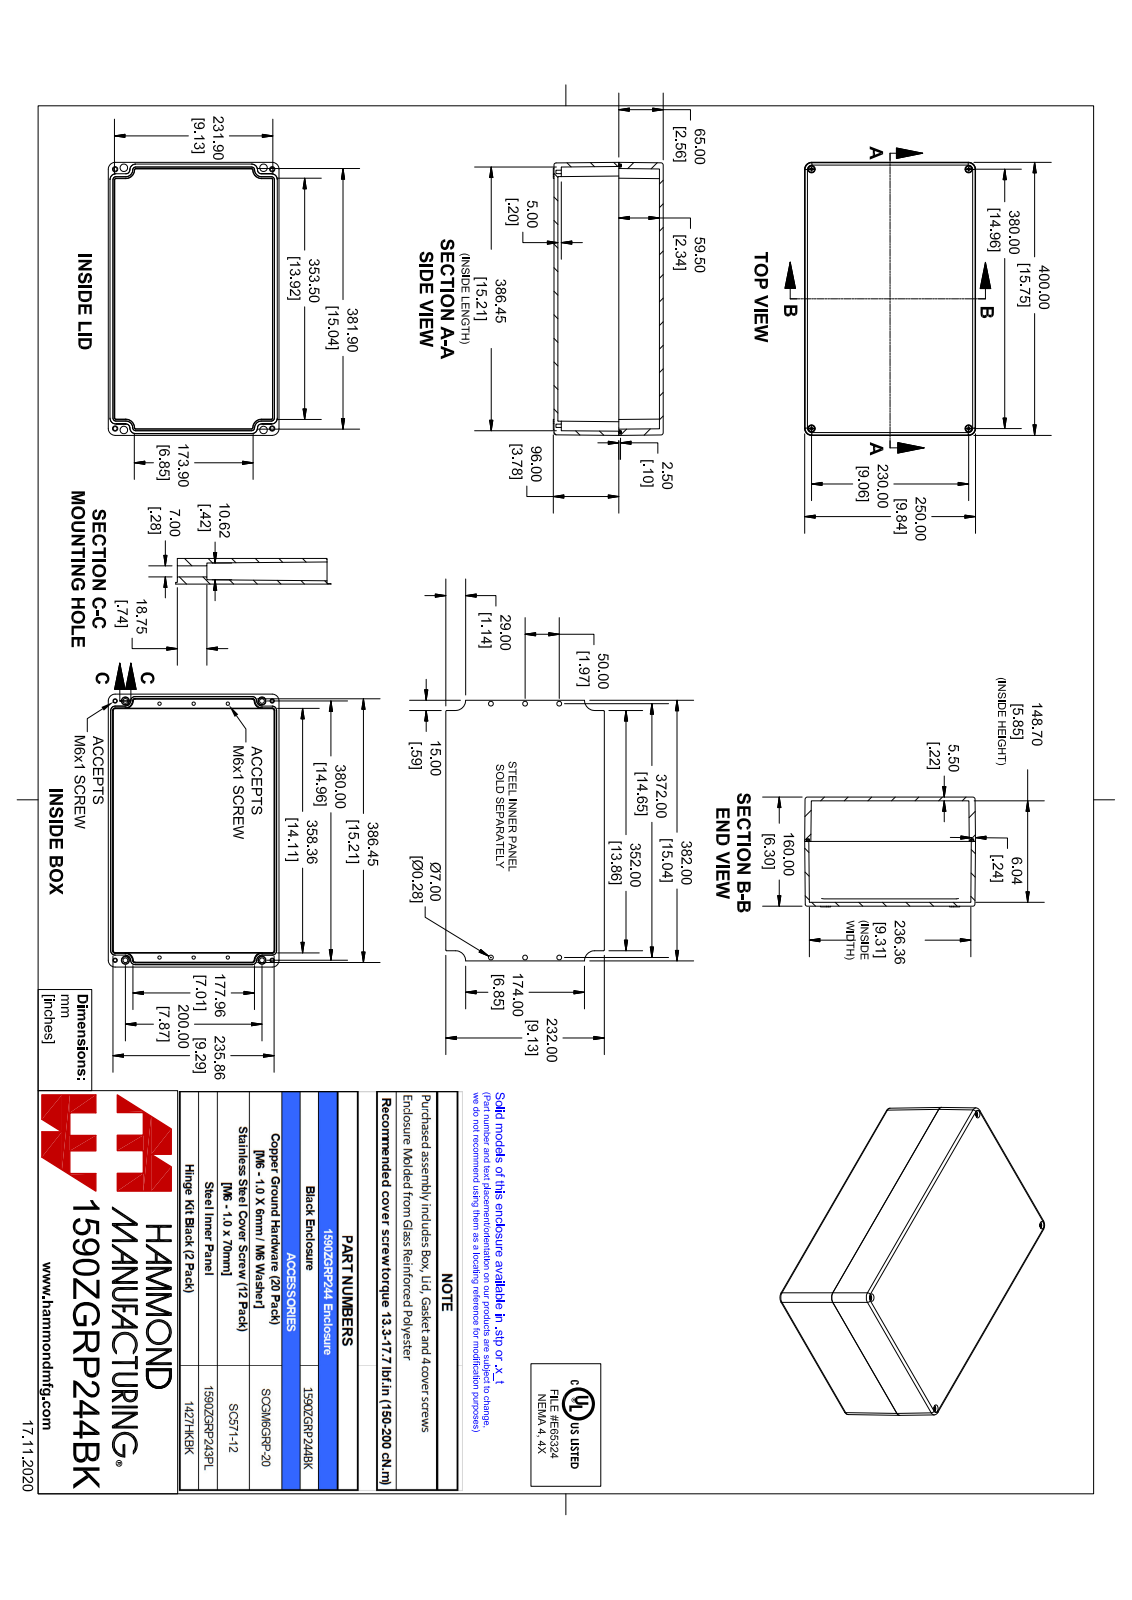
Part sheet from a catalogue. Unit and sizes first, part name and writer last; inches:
Units: inches
Overall size (bounding box): 15.748 × 9.843 × 6.339
Round holes (diameter × count): ⌀0.194 ×10, ⌀0.236 ×4, ⌀0.252 ×4, ⌀0.276 ×4, ⌀0.425 ×4, ⌀0.433 ×4
Round bosses / shafts (diameter × count): ⌀0.157 ×6, ⌀0.229 ×4, ⌀0.206 ×4
Partial cylindrical surfaces — rounded edges, fillets, slot ends (radius × count): R0.394 ×8, R0.02 ×6, R0.118 ×4, R0.138 ×4
Main face-to-face distances: 6.299, 0.238, 6.083, 0.217, 0.228, 5.854, 6.071, 0.356, 9.605, 9.843
Hole centre spacings: 0.122, 0.509, 0.591, 1.969, 1.975, 2.071, 2.564, 3.94
Volume: 163.5 in³ · Surface area: 1 294 in²
Bodies: 7 solids, 439 faces (243 planar, 68 cylindrical, 128 other)
Part name (STEP PRODUCT): 1590ZGRP244BK
STEP written by: SolidWorks 2021 (AUTOMOTIVE_DESIGN)
